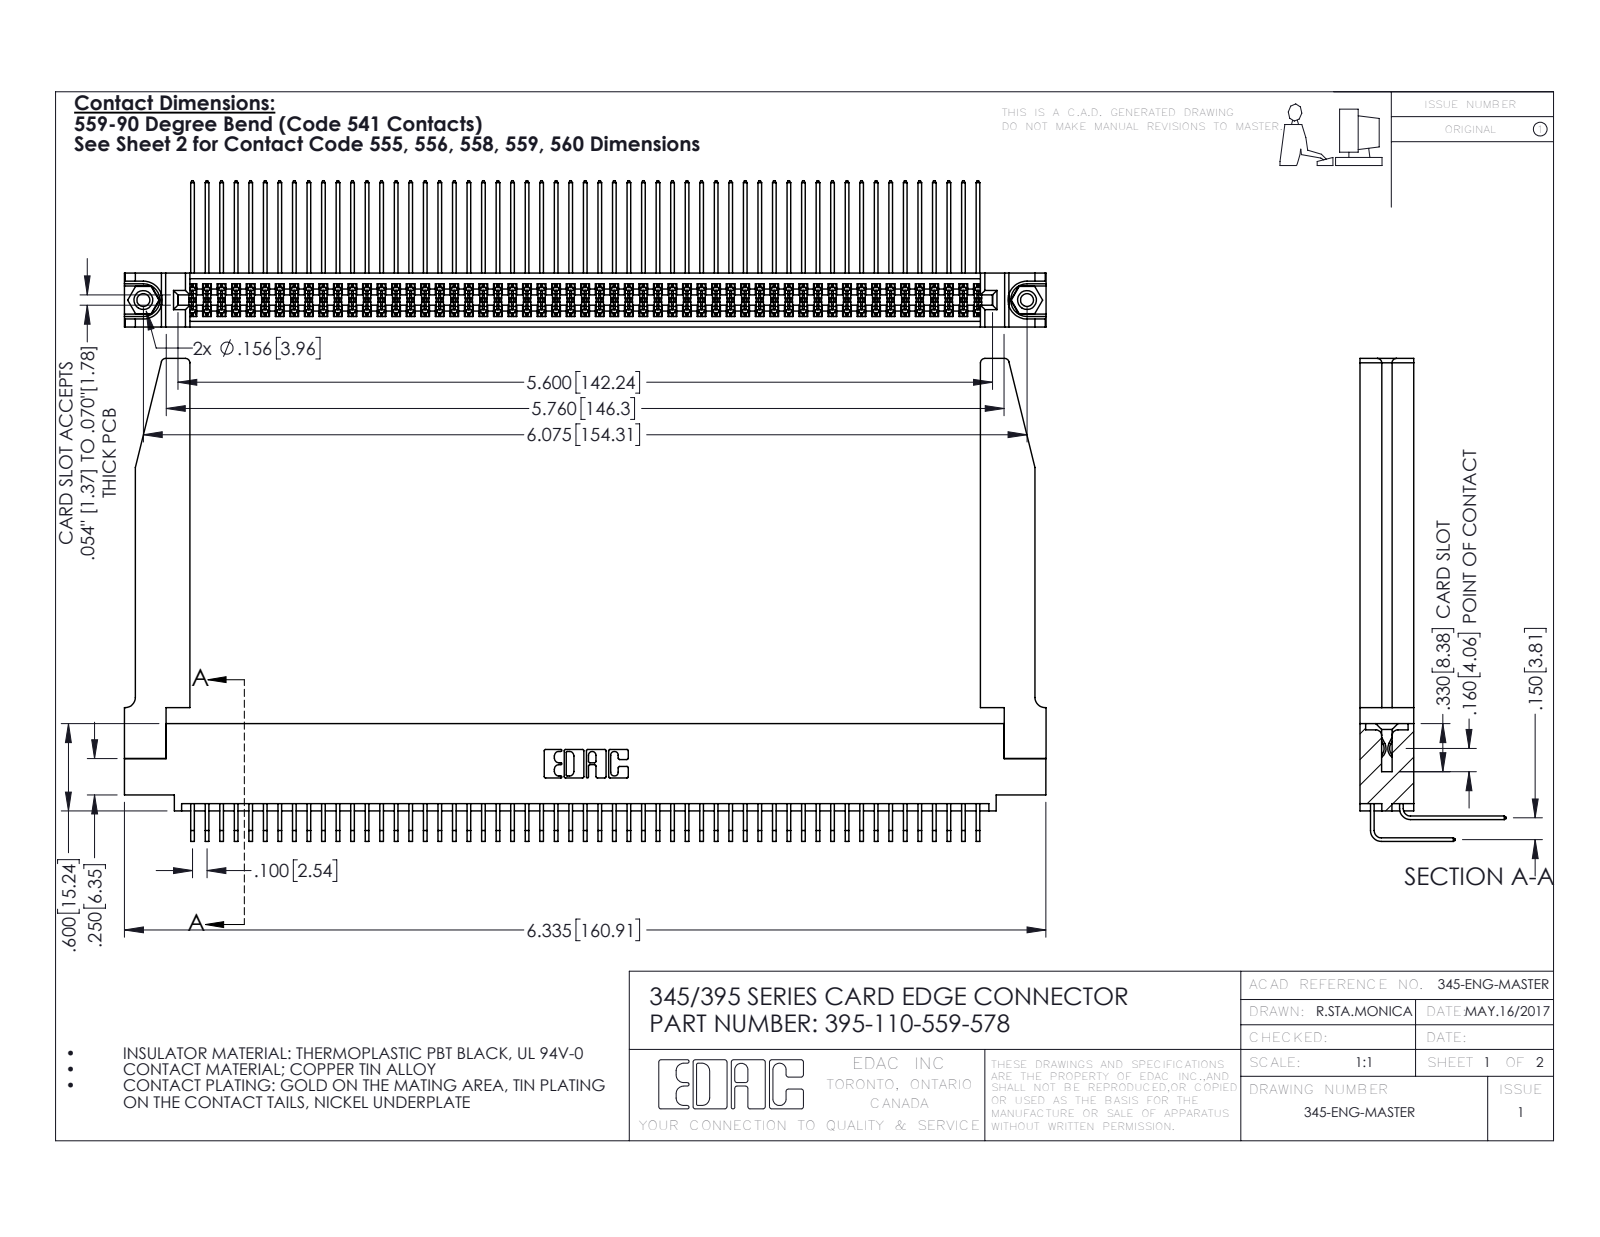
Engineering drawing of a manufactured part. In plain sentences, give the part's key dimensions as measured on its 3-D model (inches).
The part is named "345-292-001_558 559 Tail - 1; 345 Part_0.110 Offset - 0.156 Dia-TH; 345-220-078_345-220-078; 395-110-559-578 (+2 more)". Its 3-D file was written by "SolidWorks 2016 (CONFIG_CONTROL_DESIGN)". It is 115 solids with 6084 faces: 4076 planar, 1956 cylindrical and 52 other. Overall it measures 6.336 by 3.319 by 1.005 inches. Its volume is 1.47 cubic inches and its surface area 53.14 square inches. Round holes: 2 of diameter 0.089, 2 of diameter 0.125, 2 of diameter 0.156, 1 of diameter 0.064. Round bosses or shafts: 2 of diameter 0.155. Partial cylindrical surfaces (rounded edges, fillets, slot ends): 165 of radius 0.006, 22 of radius 0.01, 8 of radius 0.03, 6 of radius 0.007, 6 of radius 0.031, 3 of radius 0.026, 2 of radius 0.014, 2 of radius 0.019. The main face-to-face distances are 0.072, 0.298, 0.37, 0.2, 0.098, 0.272, 0.025, 0.225, 0.175, 0.15. The hole center spacings are 0.27, 5.839, 6.075.
